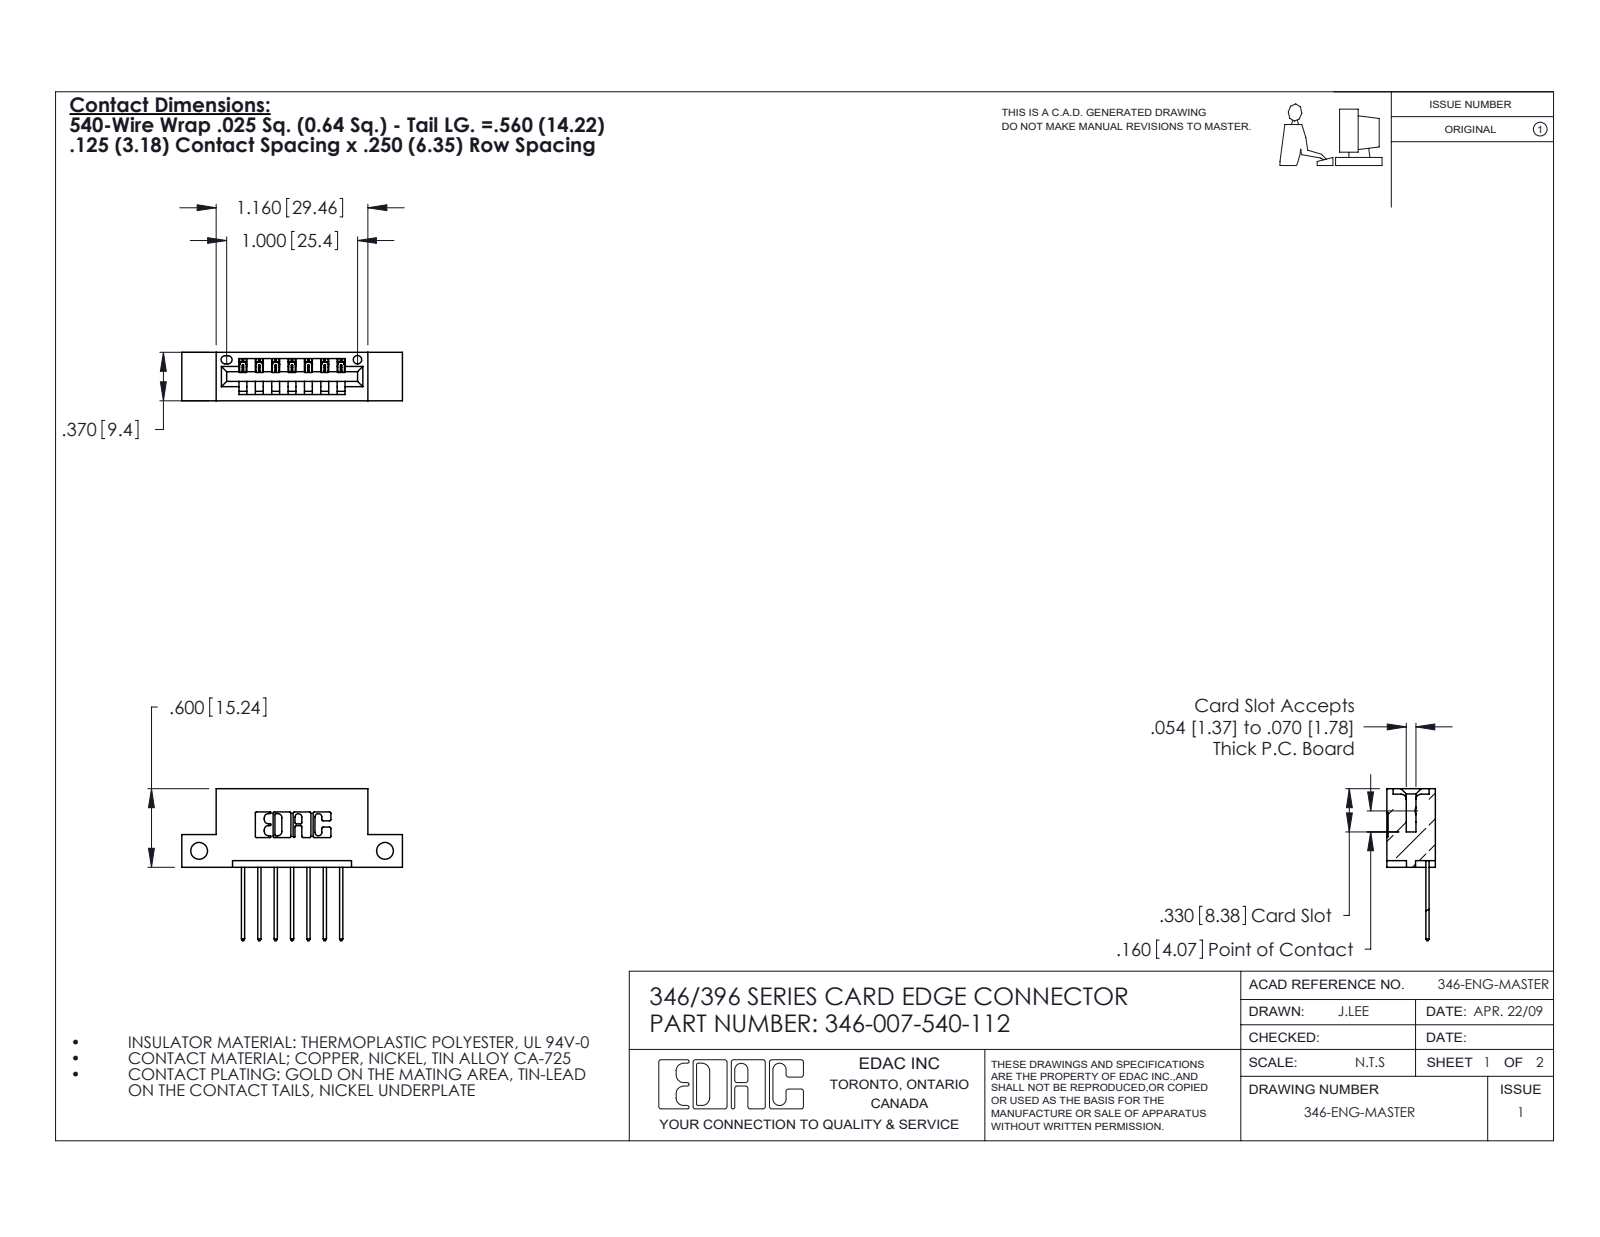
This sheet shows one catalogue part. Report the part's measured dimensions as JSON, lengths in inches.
{"part_name": "346-007-540-112; 346 Part_Flush Mounting Lugs - Side Mount; 345-292-001_345-293-140", "step_written_by": "SolidWorks 2020 (CONFIG_CONTROL_DESIGN)", "units": "inches", "bodies": {"solids": 8, "faces": 528, "planar": 356, "cylindrical": 172, "other": 0}, "overall_size": [1.685, 1.16, 0.37], "volume_in3": 0.231, "surface_area_in2": 6.615, "round_holes": [[0.128, 2], [0.064, 1]], "partial_cylinders_radius": [[0.01, 22], [0.006, 14], [0.01, 14], [0.007, 6], [0.031, 6], [0.026, 3], [0.031, 2], [0.04, 2]], "face_to_face_distances": [0.25, 0.048, 0.322, 0.37, 0.072, 0.298, 0.025, 0.148, 0.222, 0.1], "hole_center_spacings": [1.42]}
